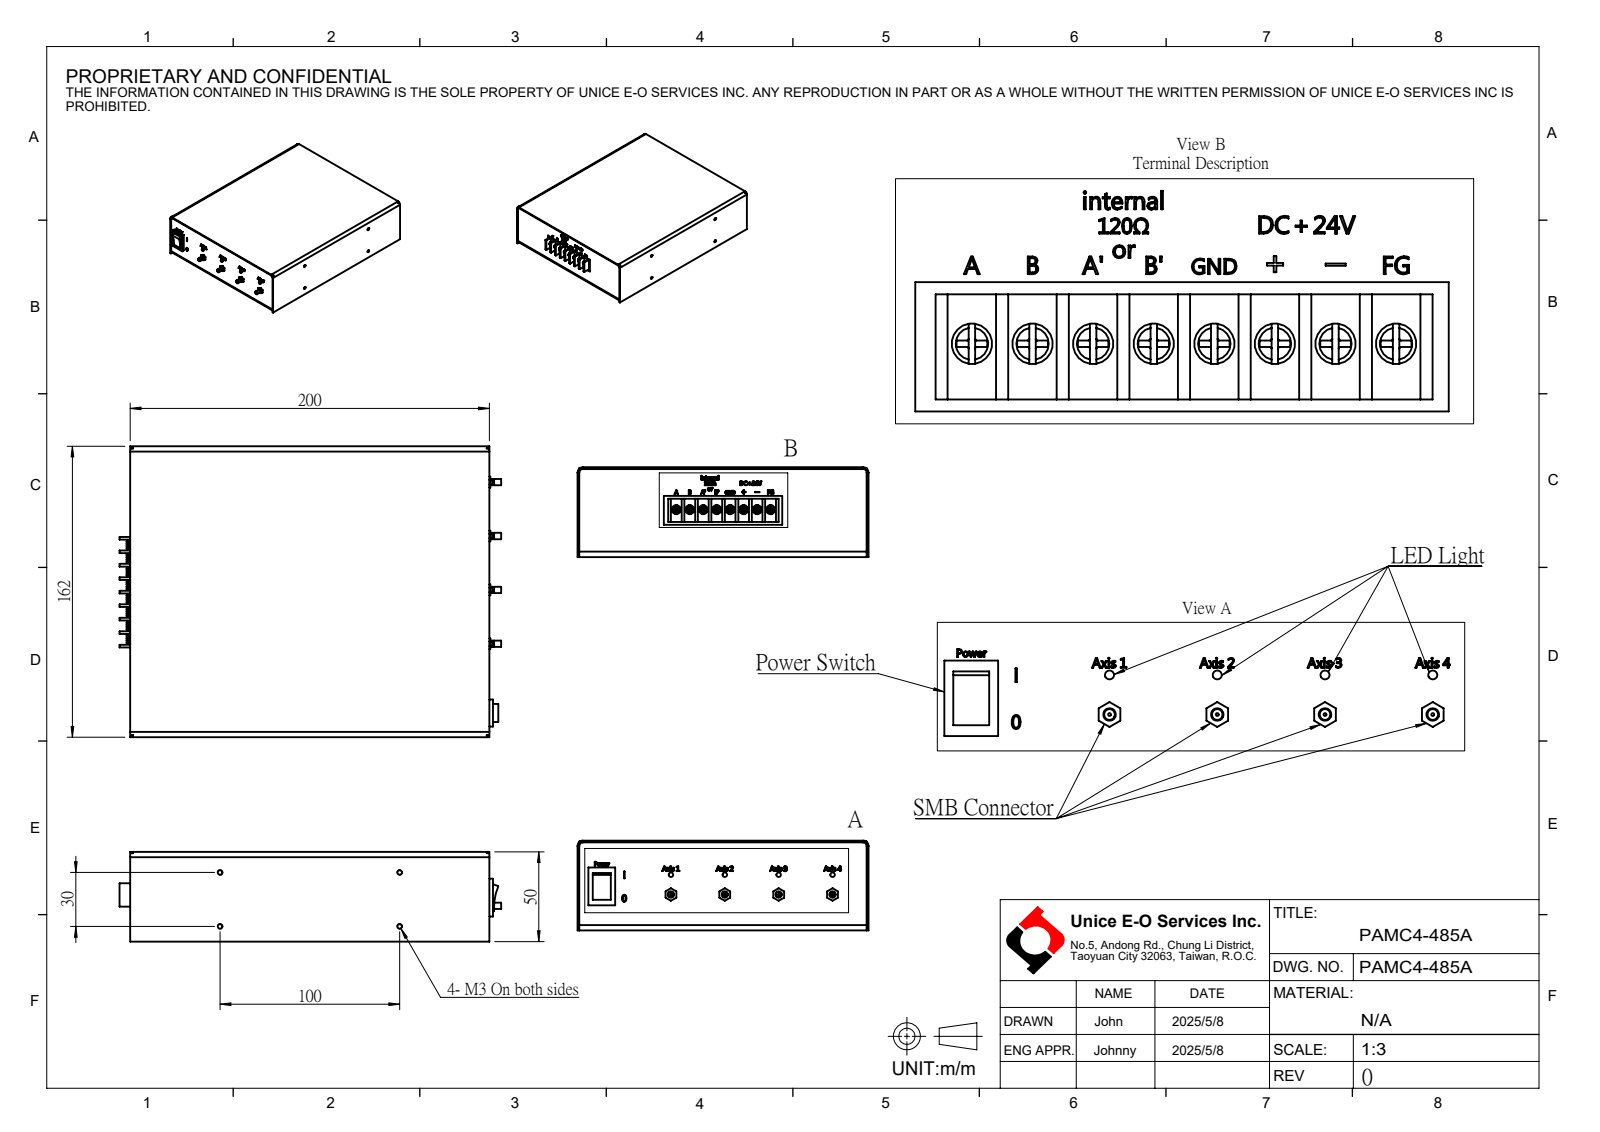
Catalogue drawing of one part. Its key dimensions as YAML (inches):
part_name: "PAMC4-485A"
step_written_by: "SolidWorks 2024 (CONFIG_CONTROL_DESIGN)"
units: inches
bodies: {solids: 1, faces: 564, planar: 374, cylindrical: 142, other: 48}
overall_size: [8.366, 6.378, 1.969]
volume: 6.143
surface_area: 310.3
round_holes:
  - {diameter: 0.098, count: 4}
  - {diameter: 0.118, count: 4}
round_bosses_or_shafts:
  - {diameter: 0.197, count: 8}
  - {diameter: 0.118, count: 8}
  - {diameter: 0.138, count: 4}
  - {diameter: 0.119, count: 4}
  - {diameter: 0.098, count: 4}
  - {diameter: 0.031, count: 4}
partial_cylinders:
  - {radius: 0.008, count: 32}
  - {radius: 0.079, count: 4}
  - {radius: 0.118, count: 4}
  - {radius: 1.378, count: 1}
face_to_face_distances: [0.039, 1.929, 1.969, 1.89, 6.339, 7.795, 6.378, 6.299, 7.756, 7.835]
hole_center_spacings: [1.181, 2.362, 3.937, 4.11, 3.543]
